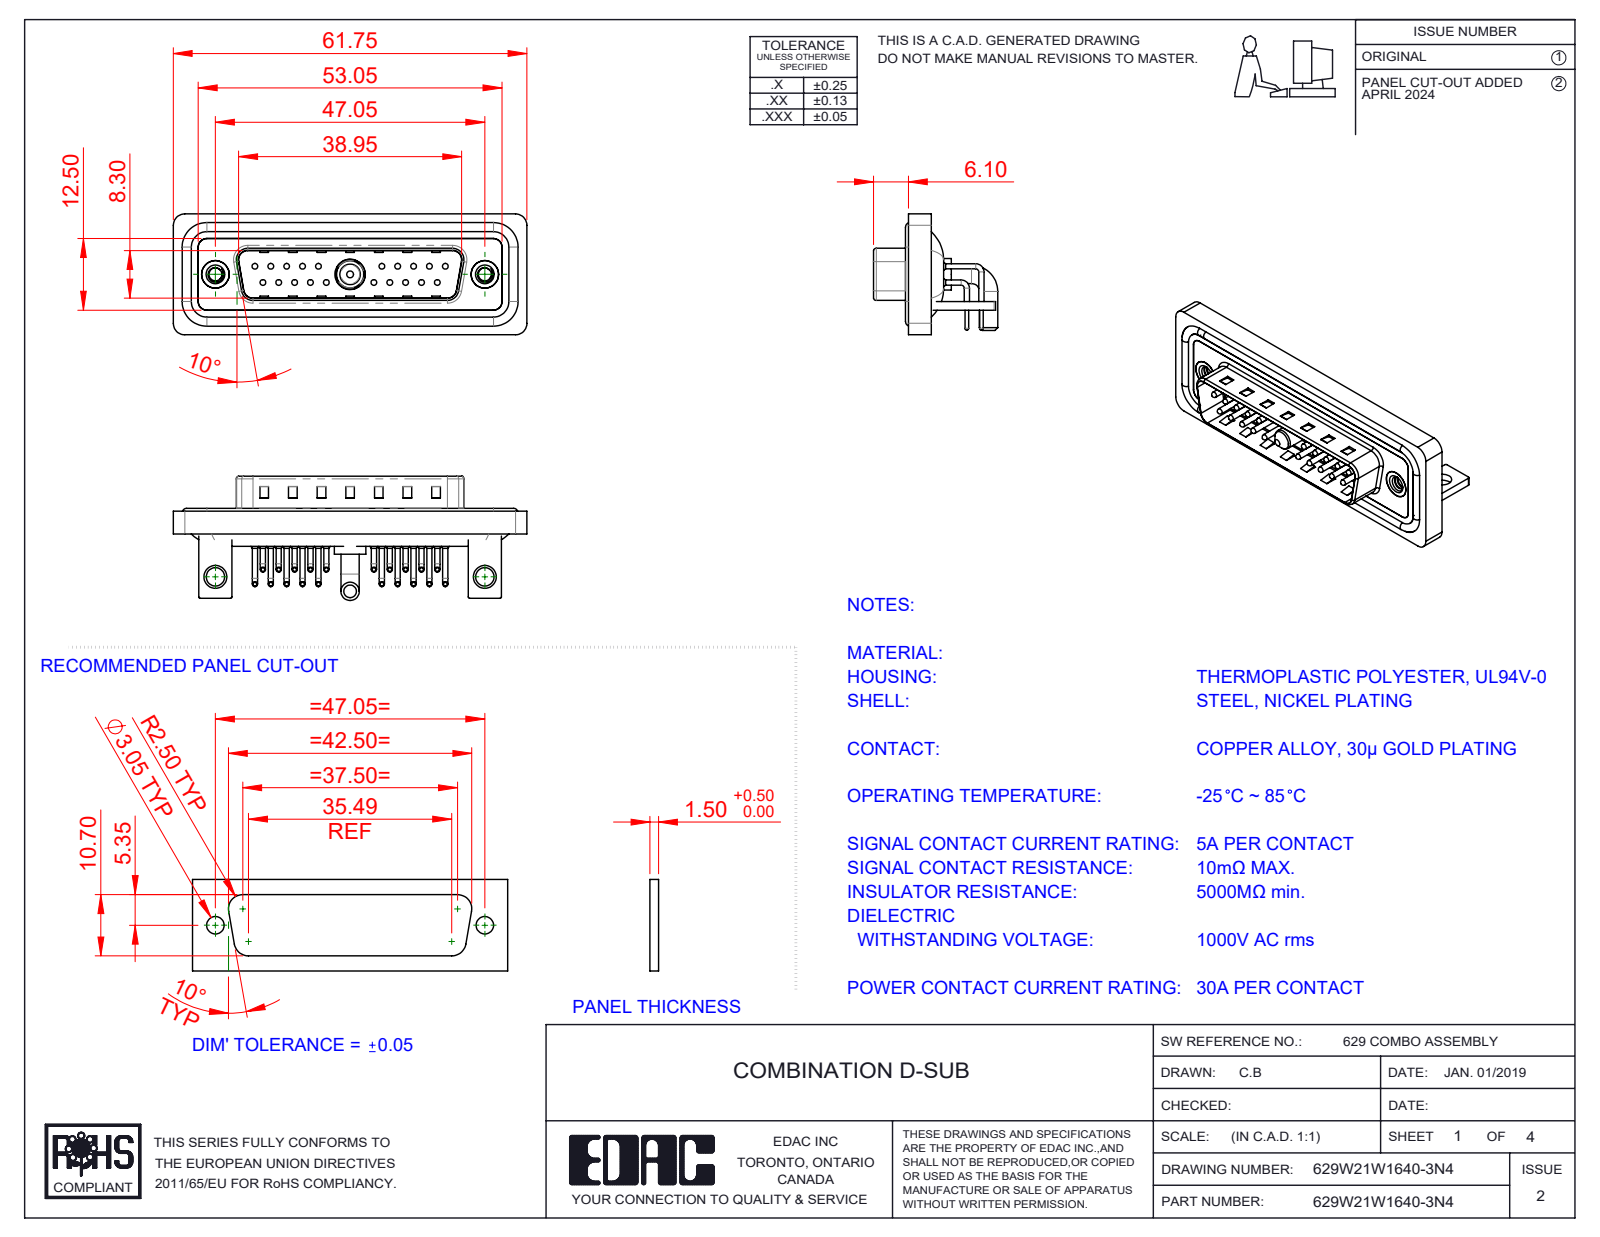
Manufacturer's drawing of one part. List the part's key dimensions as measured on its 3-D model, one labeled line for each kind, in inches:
Part name (STEP PRODUCT): 629Combo Stabilizer Bracket; 629Combo Housing_21W1; 629Combo Contact Row 2; 629Combo Shell Front_25 Contacts (+6 more)
STEP written by: SolidWorks 2023 (CONFIG_CONTROL_DESIGN)
Units: inches
Bodies: 31 solids, 2766 faces (1519 planar, 947 cylindrical, 300 other)
Overall size (bounding box): 2.431 × 0.854 × 0.831
Volume: 0.471 in³ · Surface area: 20.66 in²
Round holes (diameter × count): ⌀0.03 ×20, ⌀0.063 ×20, ⌀0.079 ×20, ⌀0.089 ×2, ⌀0.126 ×2, ⌀0.157 ×2, ⌀0.189 ×2, ⌀0.197 ×2, ⌀0.191 ×1, ⌀0.209 ×1
Round bosses / shafts (diameter × count): ⌀0.035 ×40, ⌀0.059 ×20, ⌀0.039 ×20, ⌀0.026 ×20, ⌀0.063 ×4, ⌀0.193 ×2, ⌀0.126 ×2, ⌀0.217 ×1
Partial cylindrical surfaces — rounded edges, fillets, slot ends (radius × count): R0.04 ×20, R0.079 ×19, R0.059 ×18, R0.01 ×16, R0.02 ×9, R0.063 ×8, R0.024 ×4, R0.026 ×4
Main face-to-face distances: 0.016, 0.031, 0.083, 0.114, 0.059, 0.043, 0.161, 0.063, 0.177, 0.146
Hole centre spacings: 0.124, 0.109, 0.218, 0.327, 0.198, 0.763, 0.826, 0.872
